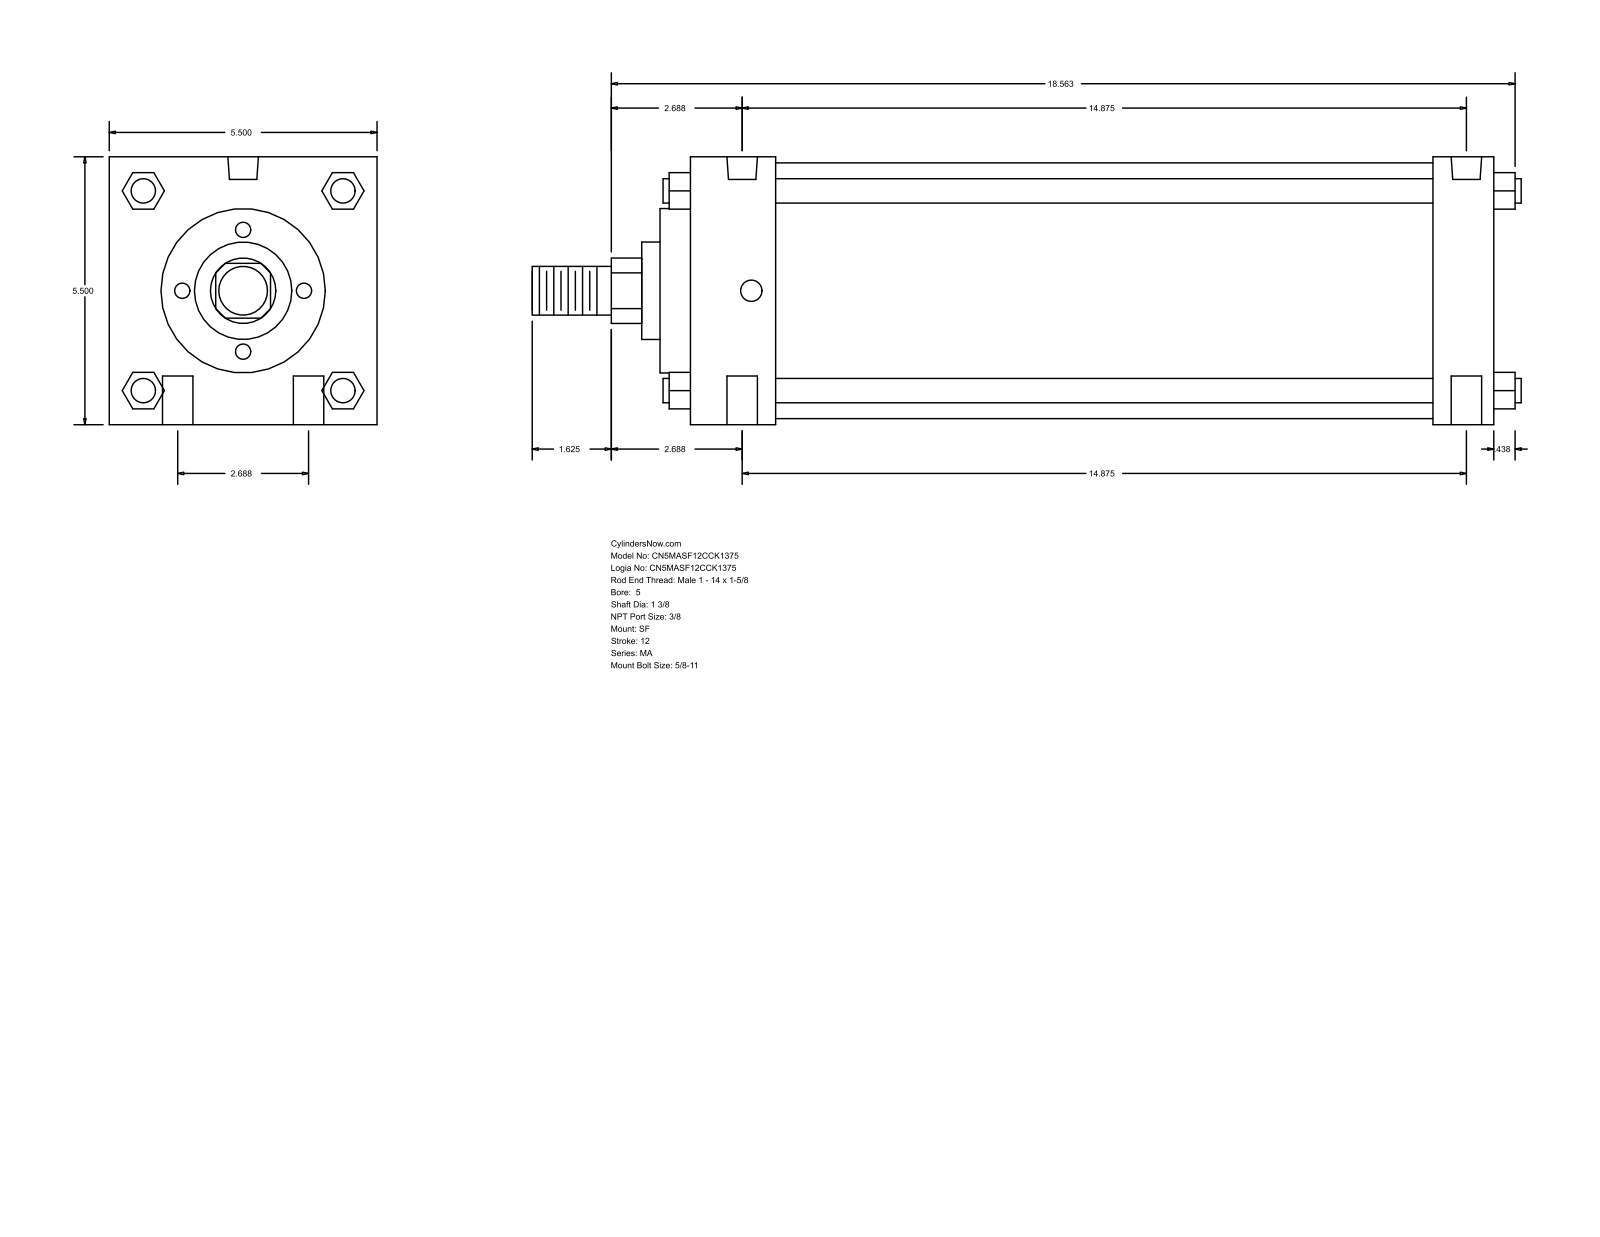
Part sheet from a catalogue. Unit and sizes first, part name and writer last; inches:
Units: inches
Overall size (bounding box): 20.313 × 5.5 × 5.5
Round holes (diameter × count): ⌀0.625 ×4, ⌀0.437 ×2, ⌀0.627 ×2
Round bosses / shafts (diameter × count): ⌀0.5 ×4, ⌀5.25 ×1, ⌀3.375 ×1, ⌀2 ×1, ⌀1.375 ×1, ⌀1 ×1
Partial cylindrical surfaces — rounded edges, fillets, slot ends (radius × count): R0.672 ×1
Main face-to-face distances: 5.5, 16.5, 1.75, 15.25, 13.5, 14.75, 1.25, 0.625, 2.375, 15.875
Hole centre spacings: 1.344, 14.936, 14.875, 2.687, 15.116, 14.5
Bodies: 0 solids, 126 faces (95 planar, 31 cylindrical, 0 other)
Part name (STEP PRODUCT): MA_SF__0500_1.375
STEP written by: GSSL Pune (CONFIG_CONTROL_DESIGN)
